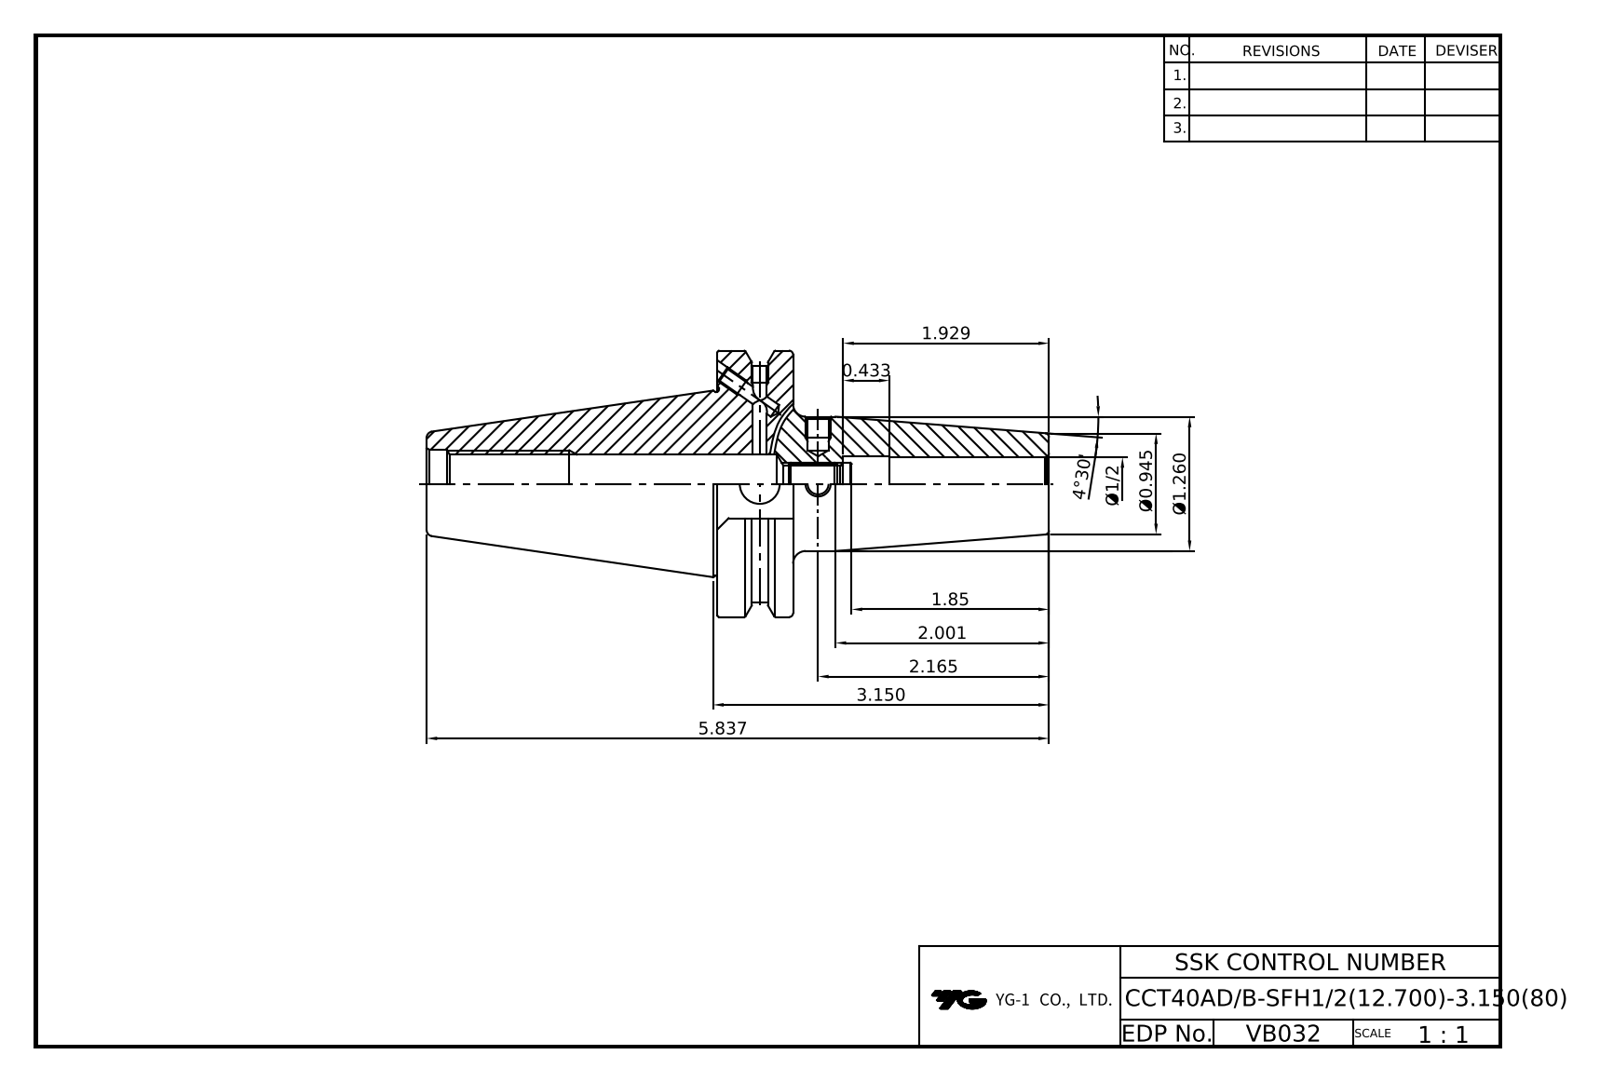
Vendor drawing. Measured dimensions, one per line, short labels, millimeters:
name: LO CCT40ADB-SFH12.7-80
written by: Autodesk Inventor 2022 (AUTOMOTIVE_DESIGN)
unit: mm
bodies: 1 solid, 89 faces (38 planar, 29 cylindrical, 22 other)
size: 148.25 × 63.5 × 61.09
volume: 136 474 mm³; area: 28 443 mm²
holes: 4× ⌀3.24, 2× ⌀4, 2× ⌀4.2, 1× ⌀8.92, 1× ⌀9.53, 1× ⌀12.7, 1× ⌀13, 1× ⌀13.39, 1× ⌀13.9, 1× ⌀16.3
bosses: 1× ⌀63.5, 1× ⌀43.8, 1× ⌀32
rounds: 1× R28.15
face distances: 18.05, 79, 60.95, 47.6, 16.38, 69.25, 87.3, 148.25, 81.34, 12.09
